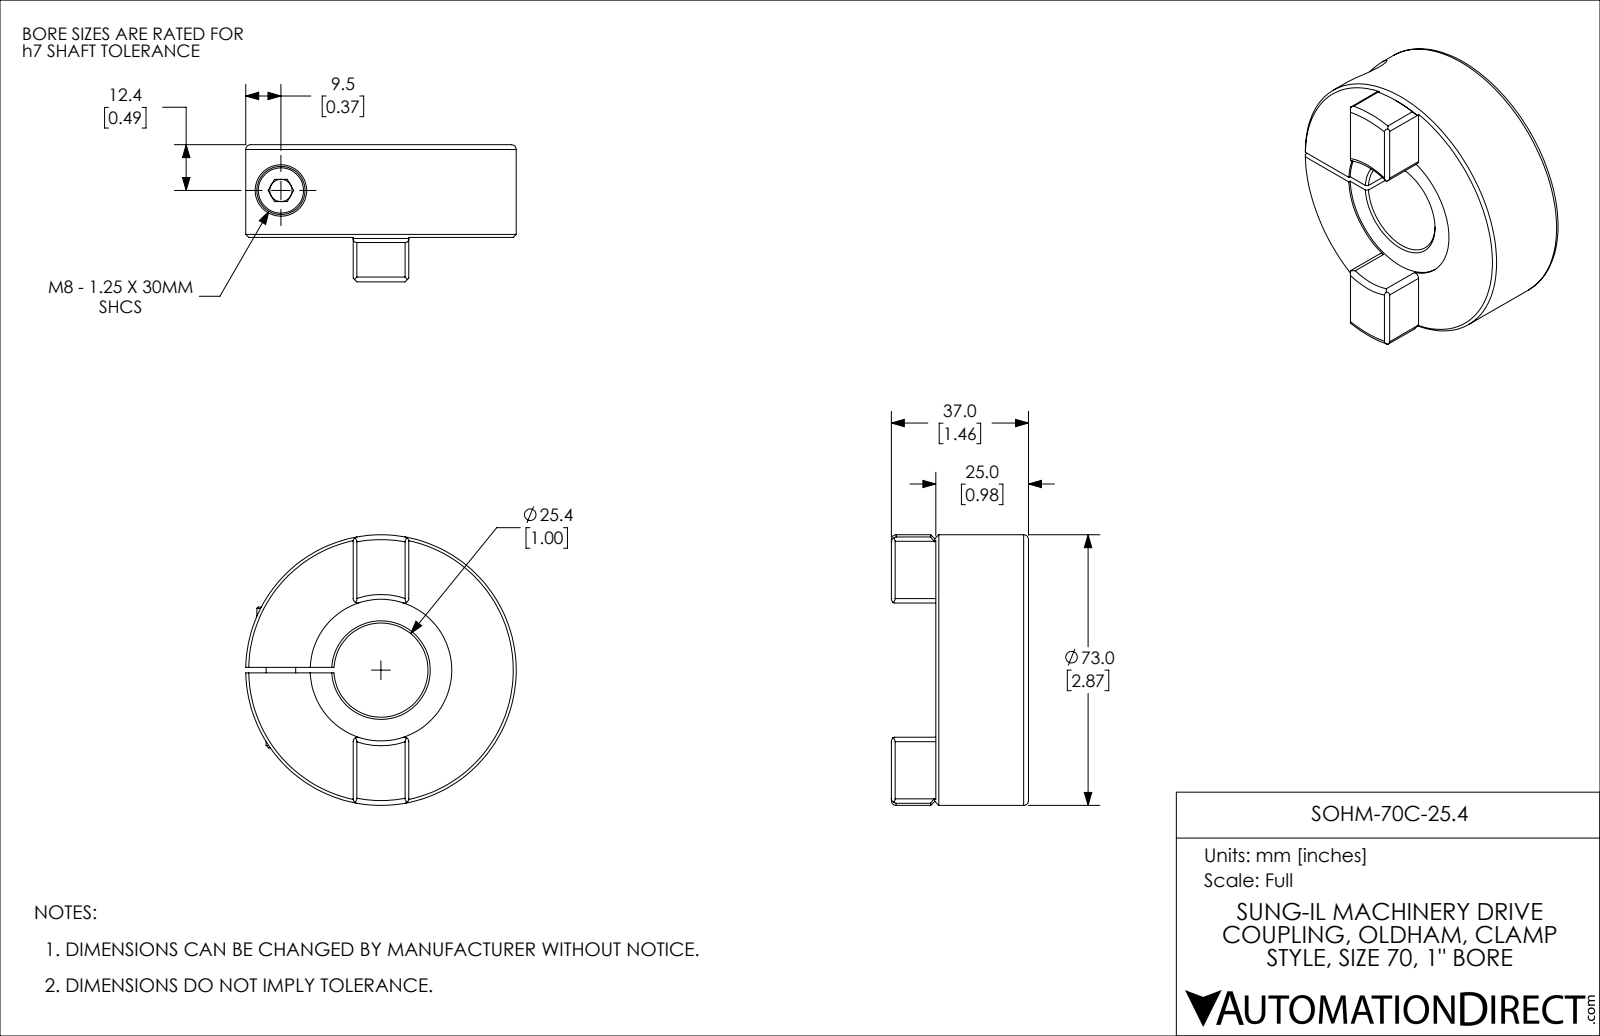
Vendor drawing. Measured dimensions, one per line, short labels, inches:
name: SOHM-70C-25.4
written by: SolidWorks 2021 (CONFIG_CONTROL_DESIGN)
unit: in
bodies: 2 solids, 94 faces (35 planar, 30 cylindrical, 29 other)
size: 2.874 × 2.874 × 1.457
volume: 5.826 in³; area: 30.96 in²
holes: 1× ⌀0.236, 1× ⌀0.268, 1× ⌀0.335, 1× ⌀0.547, 1× ⌀1, 1× ⌀1.504
bosses: 1× ⌀2.874, 1× ⌀0.512, 1× ⌀0.315
rounds: 8× R0.047, 1× R1.969
face distances: 0.984, 0.059, 0.965, 0.02, 1.457, 0.492, 0.472, 0.591, 0.384, 0.325
